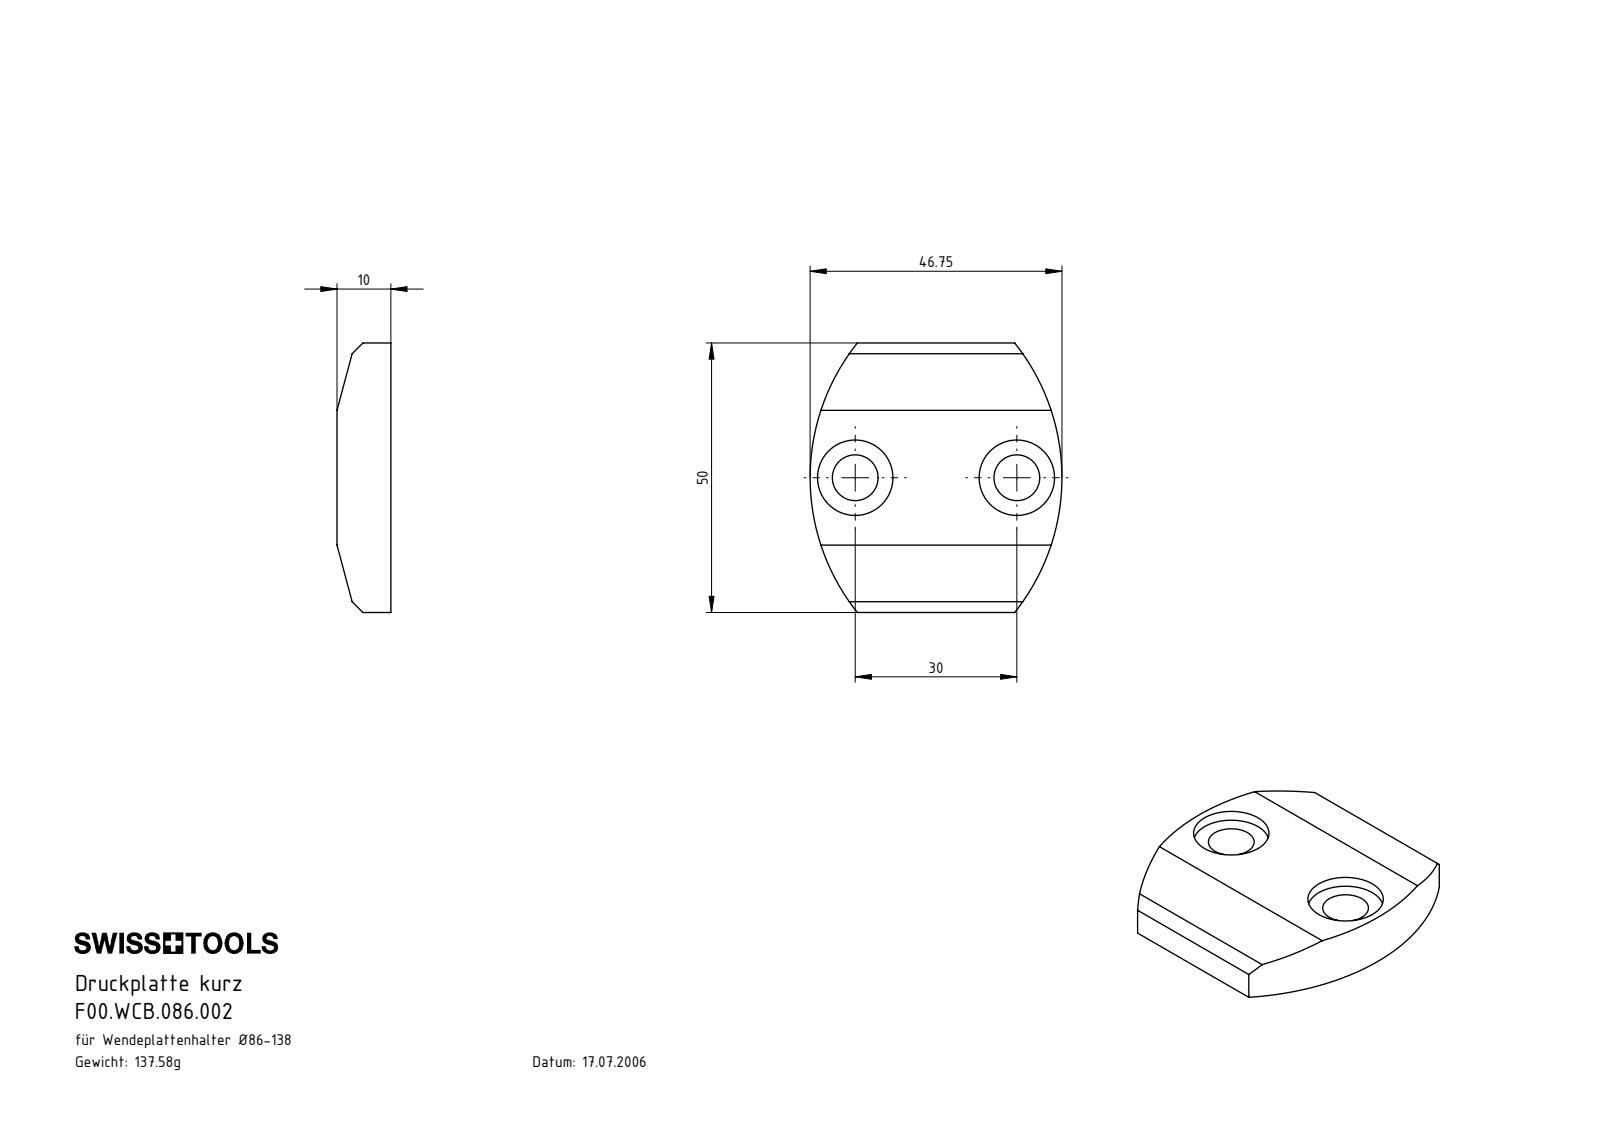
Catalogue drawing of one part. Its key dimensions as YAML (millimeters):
part_name: "F00.WCB.086.002"
step_written_by: "SolidWorks 2017 (AUTOMOTIVE_DESIGN)"
units: millimeters
bodies: {solids: 1, faces: 20, planar: 10, cylindrical: 10, other: 0}
overall_size: [50, 46.75, 10]
volume: 17527
surface_area: 5851
round_holes:
  - {diameter: 8.5, count: 2}
  - {diameter: 14, count: 2}
partial_cylinders:
  - {radius: 40, count: 2}
face_to_face_distances: [10, 8, 2, 50]
hole_center_spacings: [30]
